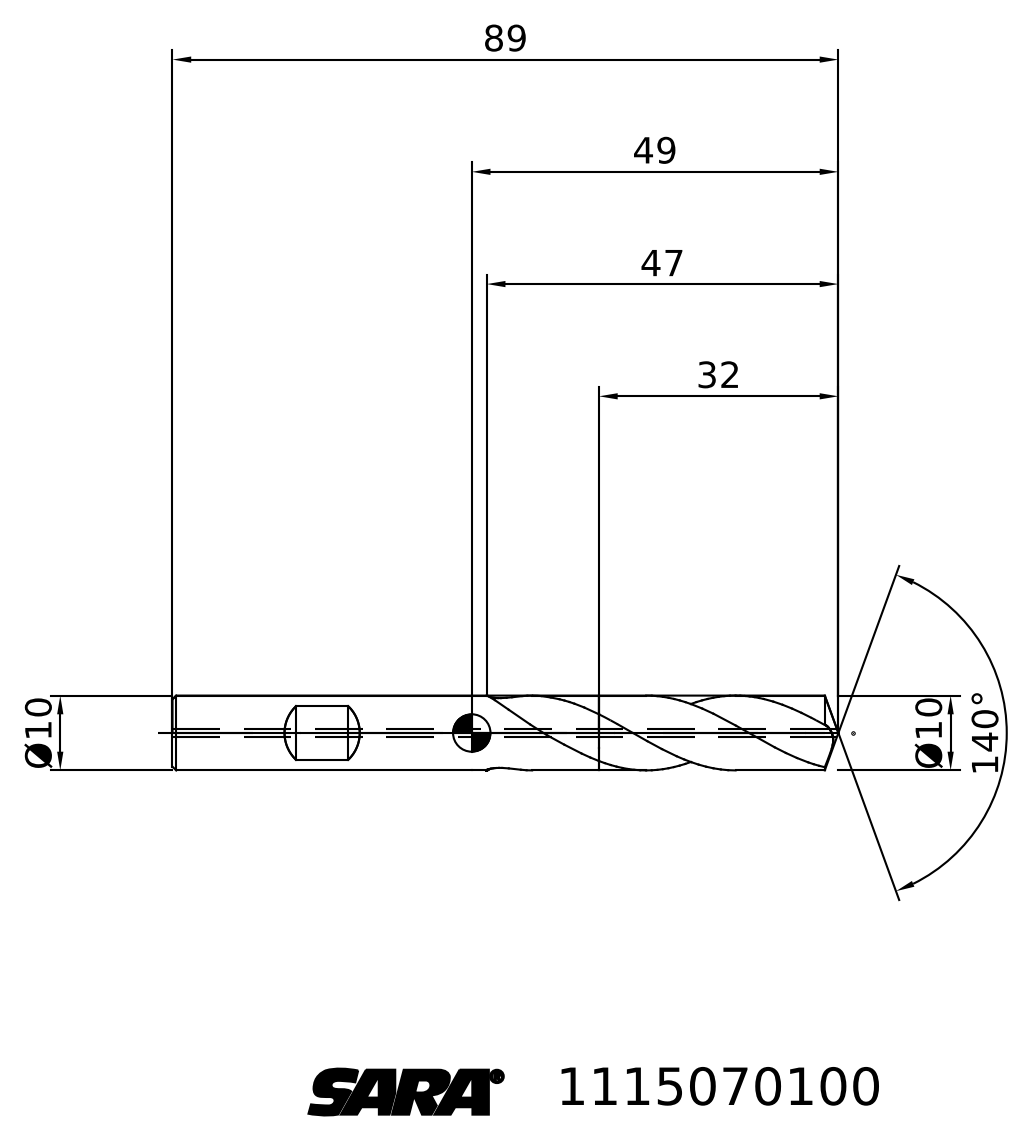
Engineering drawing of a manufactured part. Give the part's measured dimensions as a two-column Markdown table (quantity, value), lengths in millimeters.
| quantity | value |
| --- | --- |
| STEP written by | TDM (AUTOMOTIVE_DESIGN) |
| units | millimeters |
| bodies | 2 solids, 28 faces (6 planar, 0 cylindrical, 22 other) |
| overall size | 89 × 16.39 × 10 |
| volume | 5 680 mm³ |
| surface area | 3 101 mm² |
| main face-to-face distances | 57 |
